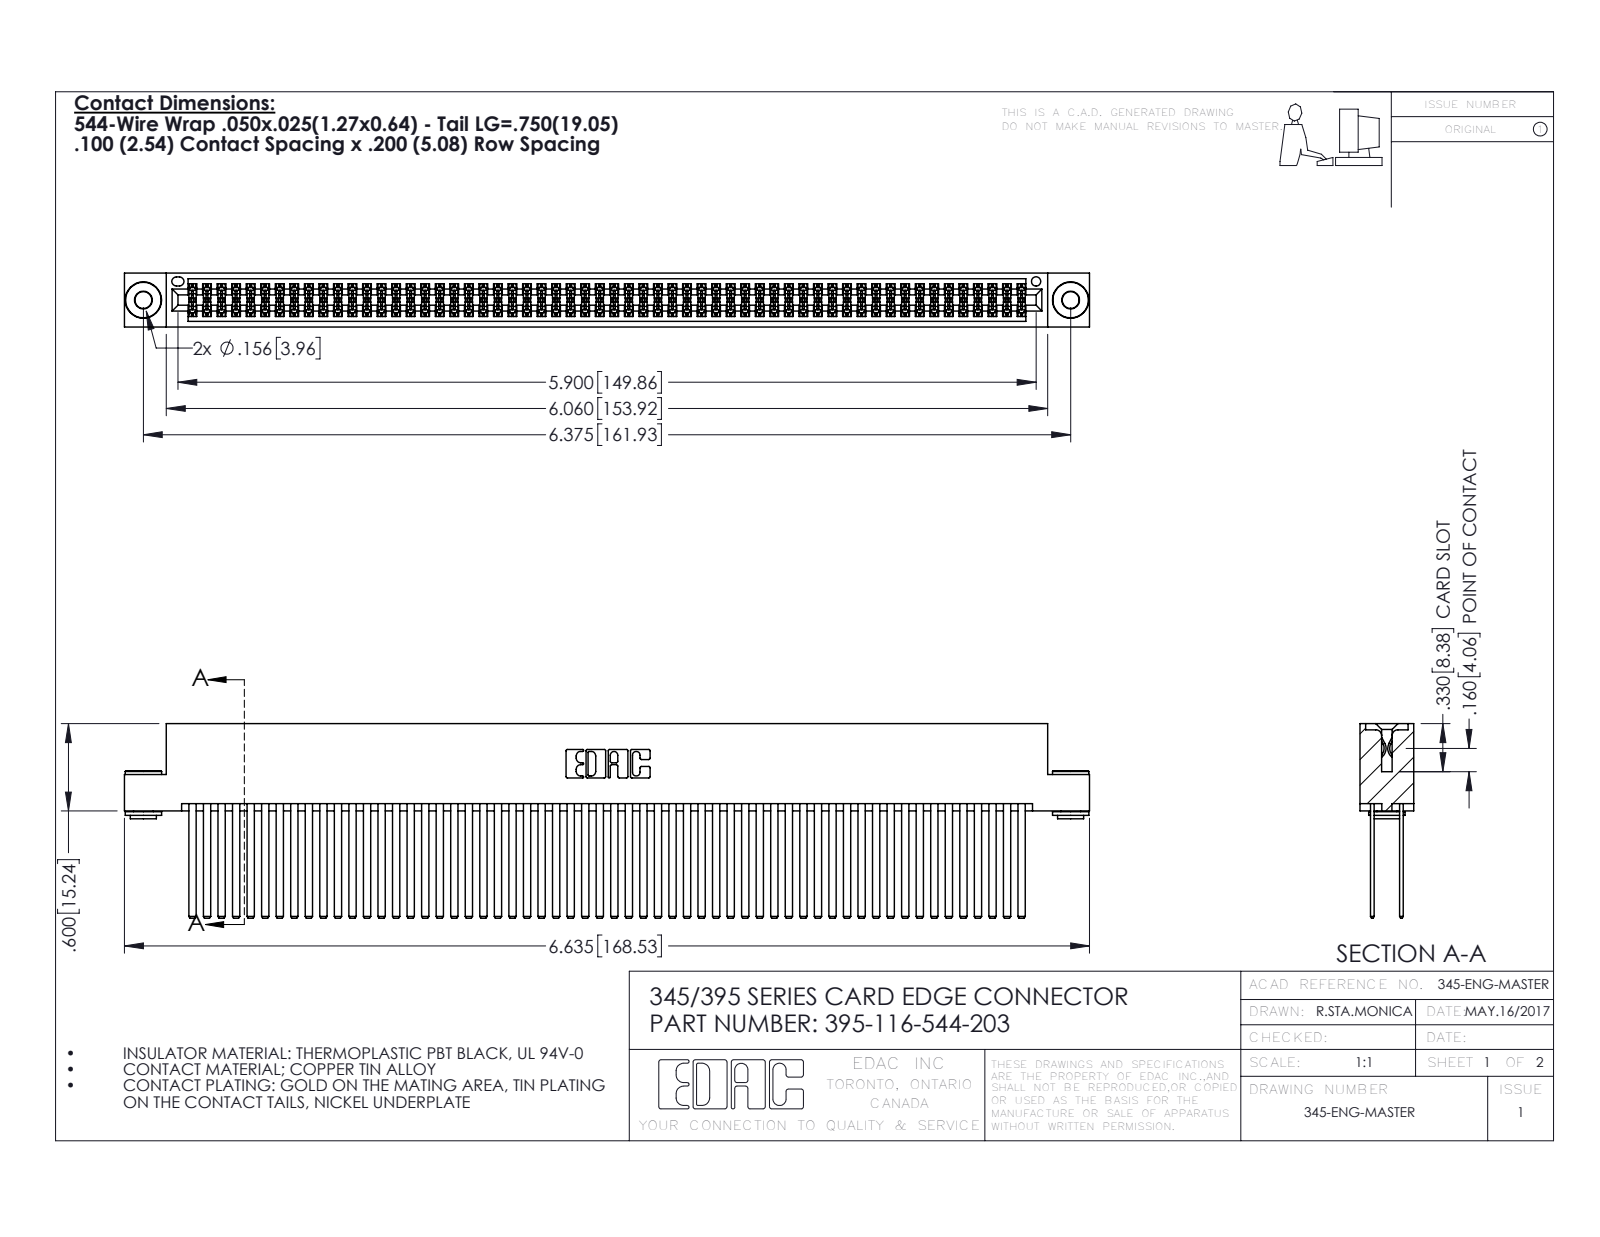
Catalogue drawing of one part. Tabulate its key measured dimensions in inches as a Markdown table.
| quantity | value |
| --- | --- |
| part name | 345-250-002_345-250-002-102; 345-292-001_345-293-144; 345 Part_Flush Mounting Lugs - 0.156 Dia-TH; 395-116-544-203 |
| STEP written by | SolidWorks 2016 (CONFIG_CONTROL_DESIGN) |
| units | inches |
| bodies | 119 solids, 5268 faces (3454 planar, 1806 cylindrical, 8 other) |
| overall size | 6.635 × 1.337 × 0.37 |
| volume | 1.109 in³ |
| surface area | 49.8 in² |
| round holes (diameter × count) | 0.116 × 2, 0.156 × 2, 0.064 × 1 |
| round bosses / shafts (diameter × count) | 0.25 × 2, 0.18 × 2, 0.136 × 2 |
| partial cylindrical surfaces (radius × count) | 0.006 × 174, 0.01 × 22, 0.007 × 6, 0.031 × 6, 0.026 × 3, 0.014 × 2, 0.019 × 2, 0.022 × 2 |
| main face-to-face distances | 0.2, 0.025, 0.072, 0.098, 0.272, 0.298, 0.225, 0.175, 0.37, 0.05 |
| hole center spacings | 0.27, 6.139, 6.375 |
